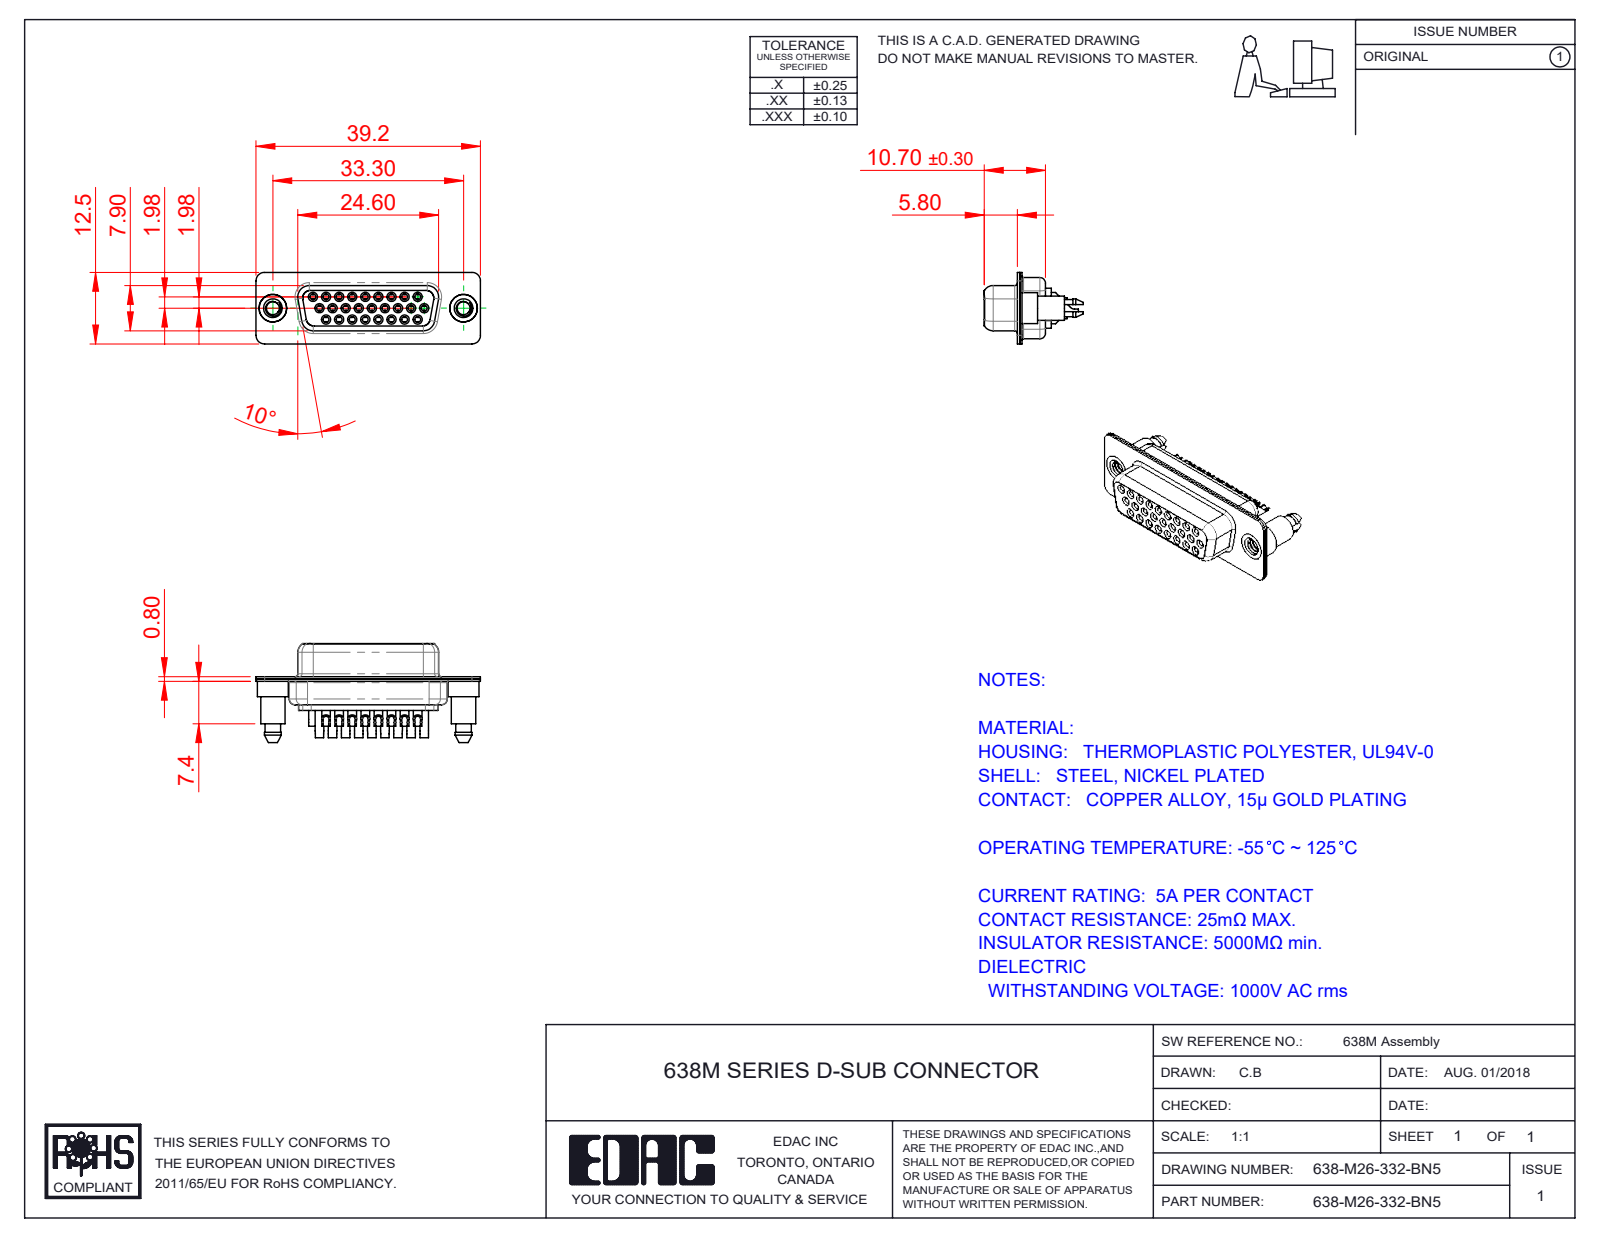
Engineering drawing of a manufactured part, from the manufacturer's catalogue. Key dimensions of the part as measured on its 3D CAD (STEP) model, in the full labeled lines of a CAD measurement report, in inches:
Part name (STEP PRODUCT): 638-M26-332-BN5; 638M Contact Row 2_32; 638M Housing_26 Contacts; 638M Shell Front_26 Contacts (+4 more)
STEP written by: SolidWorks 2020 (CONFIG_CONTROL_DESIGN)
Units: inches
Bodies: 31 solids, 1759 faces (525 planar, 715 cylindrical, 519 other)
Overall size (bounding box): 1.543 × 0.681 × 0.492
Volume: 0.154 in³ · Surface area: 12.99 in²
Round holes (diameter × count): ⌀0.039 ×27, ⌀0.043 ×26, ⌀0.067 ×26, ⌀0.071 ×26, ⌀0.079 ×26, ⌀0.089 ×2, ⌀0.157 ×2, ⌀0.189 ×2
Round bosses / shafts (diameter × count): ⌀0.087 ×26, ⌀0.063 ×26, ⌀0.059 ×26, ⌀0.213 ×2, ⌀0.193 ×2, ⌀0.167 ×2
Partial cylindrical surfaces — rounded edges, fillets, slot ends (radius × count): R0.059 ×18, R0.079 ×12, R0.063 ×10, R0.053 ×8, R0.039 ×7, R0.01 ×4, R0.02 ×4, R0.024 ×4
Main face-to-face distances: 0.016, 0.055, 0.018, 0.333, 0.35, 0.039, 0.071, 0.244, 0.278, 0.073
Hole centre spacings: 0.156, 0.09, 0.18, 0.238, 0.09, 0.324, 0.27, 0.238
